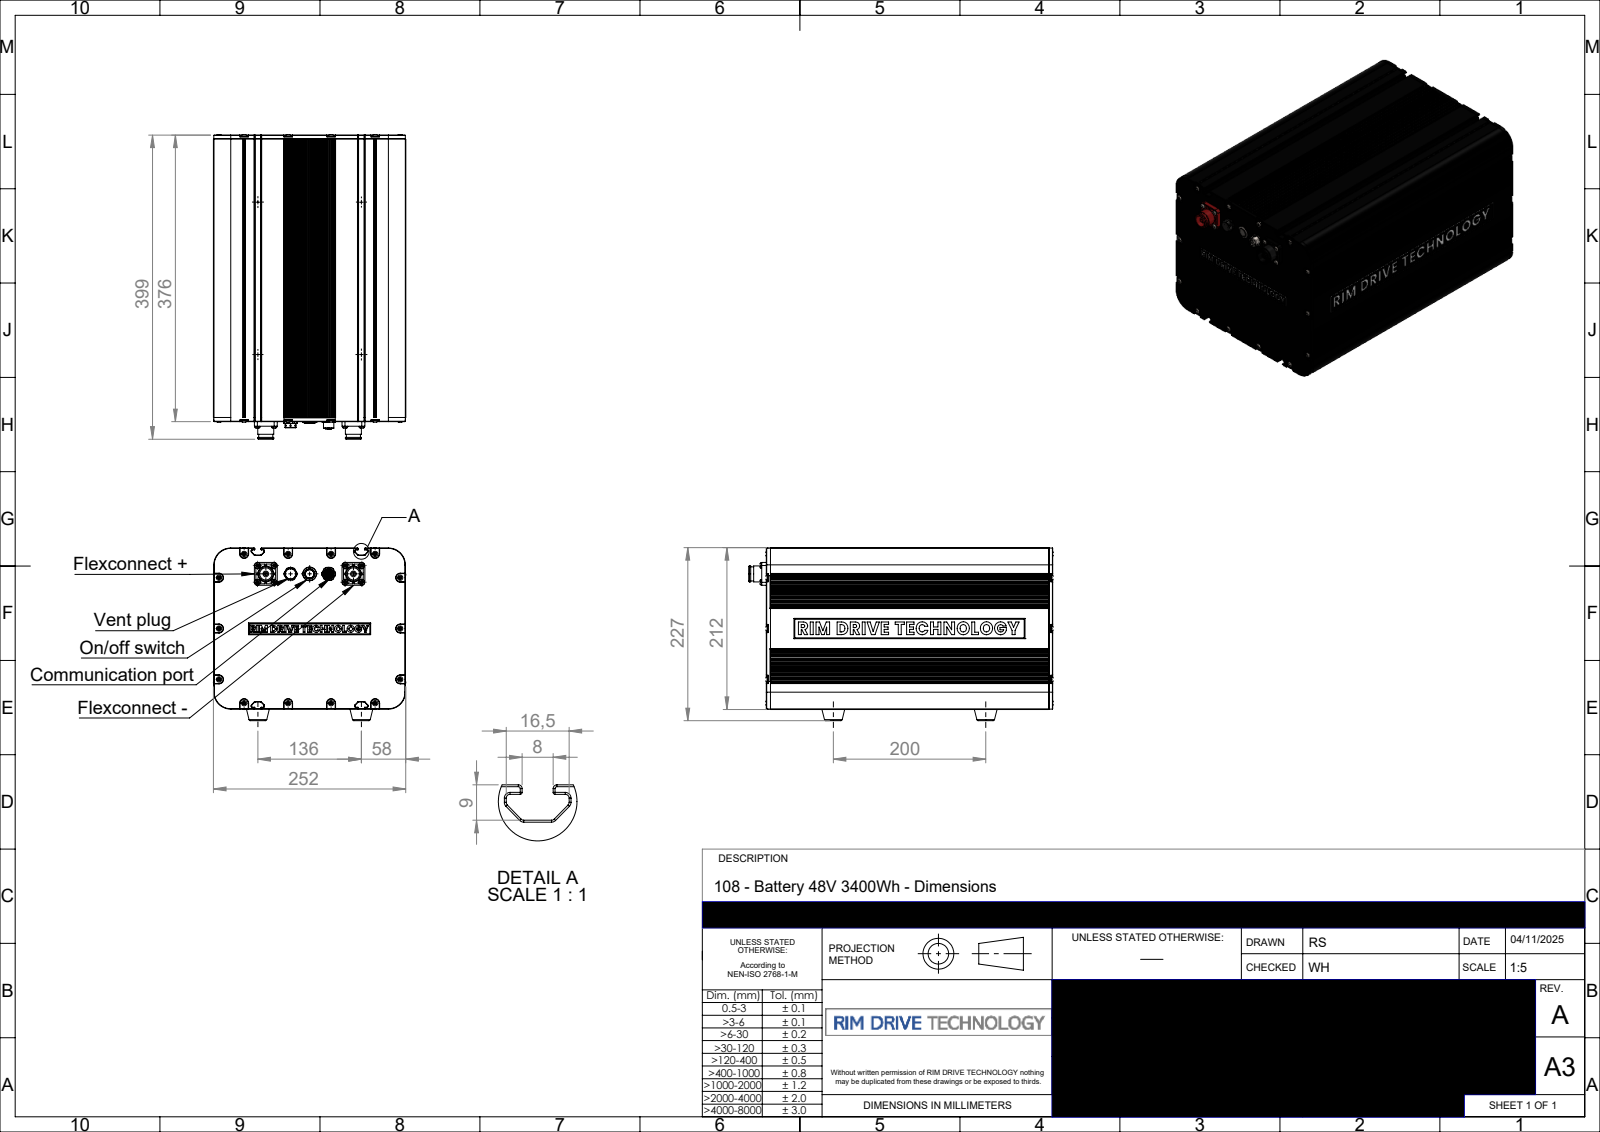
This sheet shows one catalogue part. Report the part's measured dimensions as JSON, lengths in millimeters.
{"part_name": "P-108-201-rev-A-48V 3400Wh", "step_written_by": "SolidWorks 2024 (AUTOMOTIVE_DESIGN)", "units": "millimeters", "bodies": {"solids": 1, "faces": 4104, "planar": 1829, "cylindrical": 1340, "other": 935}, "overall_size": [399.6, 252.36, 227.1], "volume_mm3": 19620000, "surface_area_mm2": 550341, "round_holes": [[1.1, 4], [10.6, 4], [2, 3], [16, 2], [7.3, 1], [11.47, 1], [11.8, 1]], "round_bosses_or_shafts": [[7, 22], [9.5, 4], [21, 2], [18.6, 2], [7.5, 2], [17.8, 1], [14.5, 1], [13.57, 1]], "partial_cylinders_radius": [[0.5, 292], [0.34, 84], [0.59, 84], [0.29, 48], [0.69, 48], [1, 32], [0.45, 24], [0.79, 24]], "face_to_face_distances": [211.4, 376, 2.5, 251.36, 0.5, 250.86, 208.9, 250.36, 5, 7.5], "hole_center_spacings": [2.33, 3.3, 4.67, 23.41, 25, 26.7, 30.89, 32.5]}
